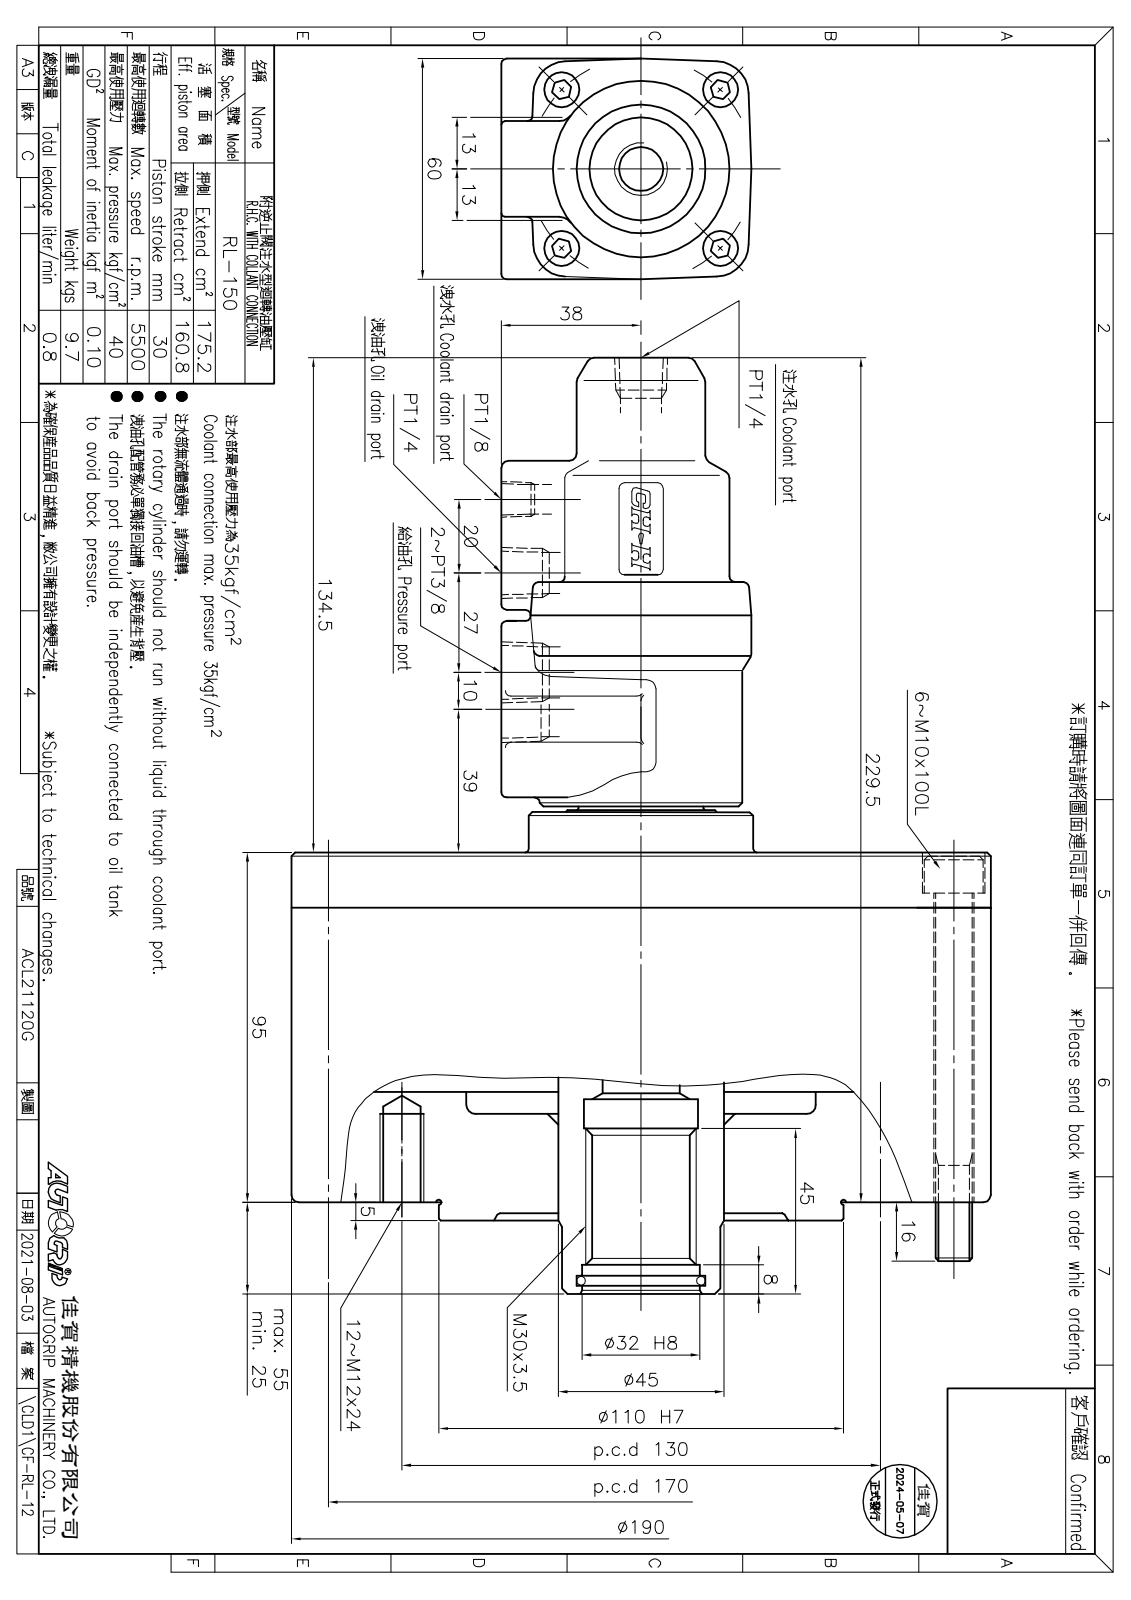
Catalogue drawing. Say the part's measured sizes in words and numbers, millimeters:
The part is named "RK-150缸體; RL-150活塞; RL-150組合件". Its 3-D file was written by "SolidWorks 2010 (CONFIG_CONTROL_DESIGN)". It is 5 solids with 443 faces: 86 planar, 172 cylindrical and 185 other. Overall it measures 254.5 by 190 by 190 millimeters. Its volume is 2 471 000 cubic millimeters and its surface area 334 760 square millimeters. Round holes: 12 of diameter 10.2, 12 of diameter 12, 6 of diameter 11, 6 of diameter 17, 2 of diameter 11.2, 2 of diameter 14.7, 1 of diameter 8.3, 1 of diameter 30, 1 of diameter 31, 1 of diameter 32, 1 of diameter 45. Round bosses or shafts: 1 of diameter 190, 1 of diameter 150, 1 of diameter 110, 1 of diameter 61, 1 of diameter 55, 1 of diameter 48, 1 of diameter 43, 1 of diameter 35. Partial cylindrical surfaces (rounded edges, fillets, slot ends): 24 of radius 1.5, 4 of radius 6, 4 of radius 9, 3 of radius 2, 2 of radius 5, 2 of radius 15. The main face-to-face distances are 30, 65, 35, 22, 15, 7, 43, 20, 60, 73. The hole center spacings are 65, 85, 112.59, 148.74, 27.87, 33.65, 60.3, 91.93.
